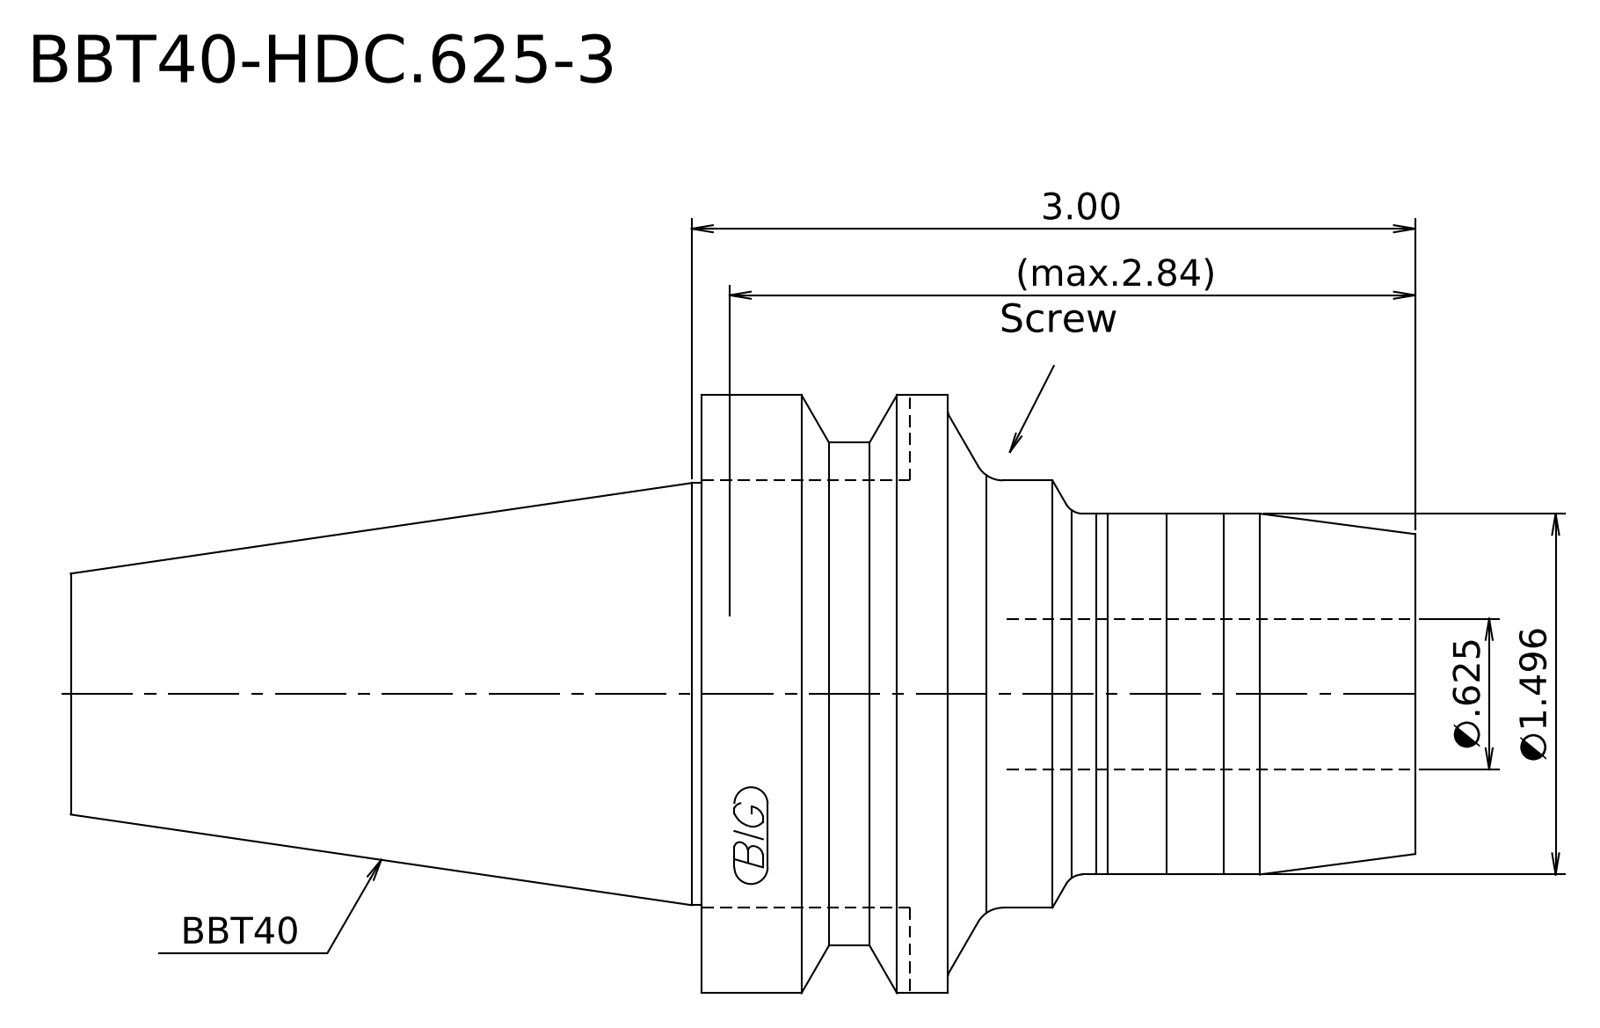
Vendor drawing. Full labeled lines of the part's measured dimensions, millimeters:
STEP written by: Kubotek KeyCreator 2011 V10.0.2 (22737) (automotive_design)
Units: millimetres
Bodies: 1 solid, 17 faces (4 planar, 6 cylindrical, 7 other)
Overall size (bounding box): 141.6 × 63 × 63
Volume: 202 717 mm³ · Surface area: 23 638 mm²
Round bosses / shafts (diameter × count): ⌀63 ×1, ⌀53 ×1, ⌀45 ×1, ⌀44.45 ×1, ⌀38 ×1
Main face-to-face distances: 75.2, 141.6, 66.4, 49.2, 26, 92.4
